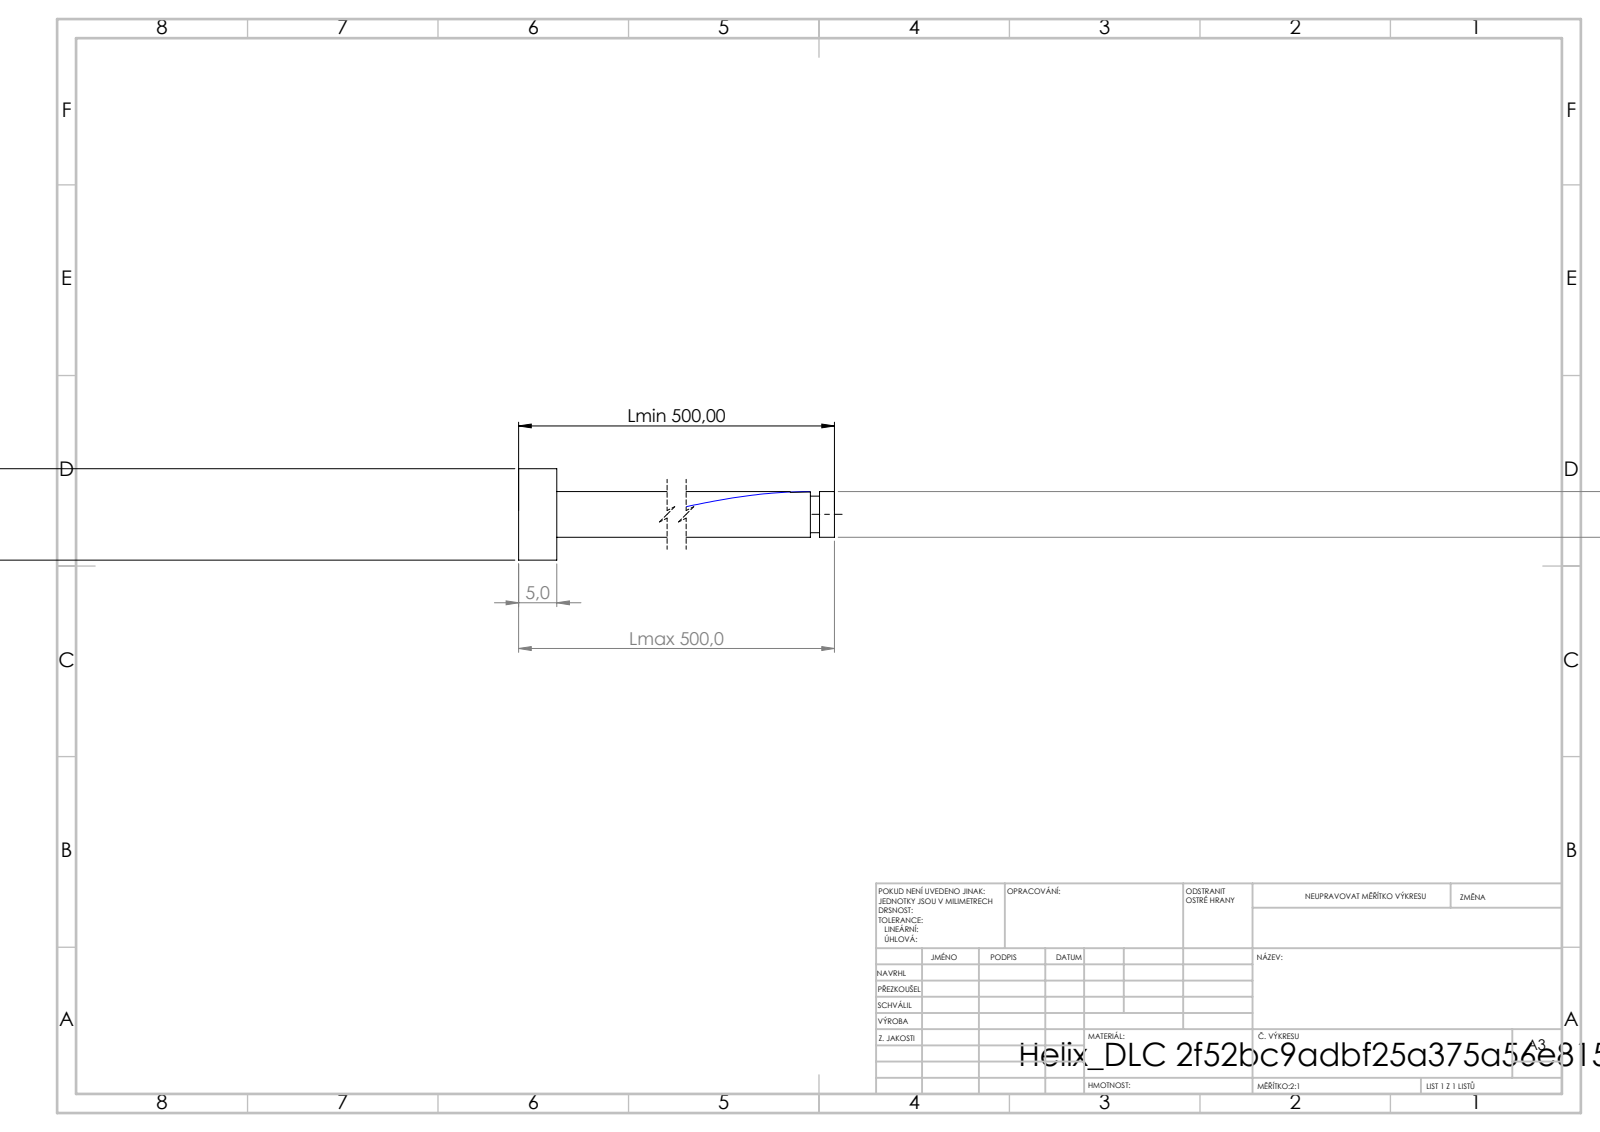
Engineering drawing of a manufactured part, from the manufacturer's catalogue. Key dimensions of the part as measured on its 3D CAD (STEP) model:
STEP written by: SolidWorks 2019 (CONFIG_CONTROL_DESIGN)
Units: millimetres
Bodies: 1 solid, 16 faces (6 planar, 9 cylindrical, 1 other)
Overall size (bounding box): 500 × 12 × 12
Volume: 17 555 mm³ · Surface area: 13 048 mm²
Round bosses / shafts (diameter × count): ⌀12 ×1, ⌀6 ×1, ⌀4.8 ×1
Main face-to-face distances: 5, 500, 495, 498.04, 493.04, 1.96, 496.84, 491.84, 1.2, 3.16
